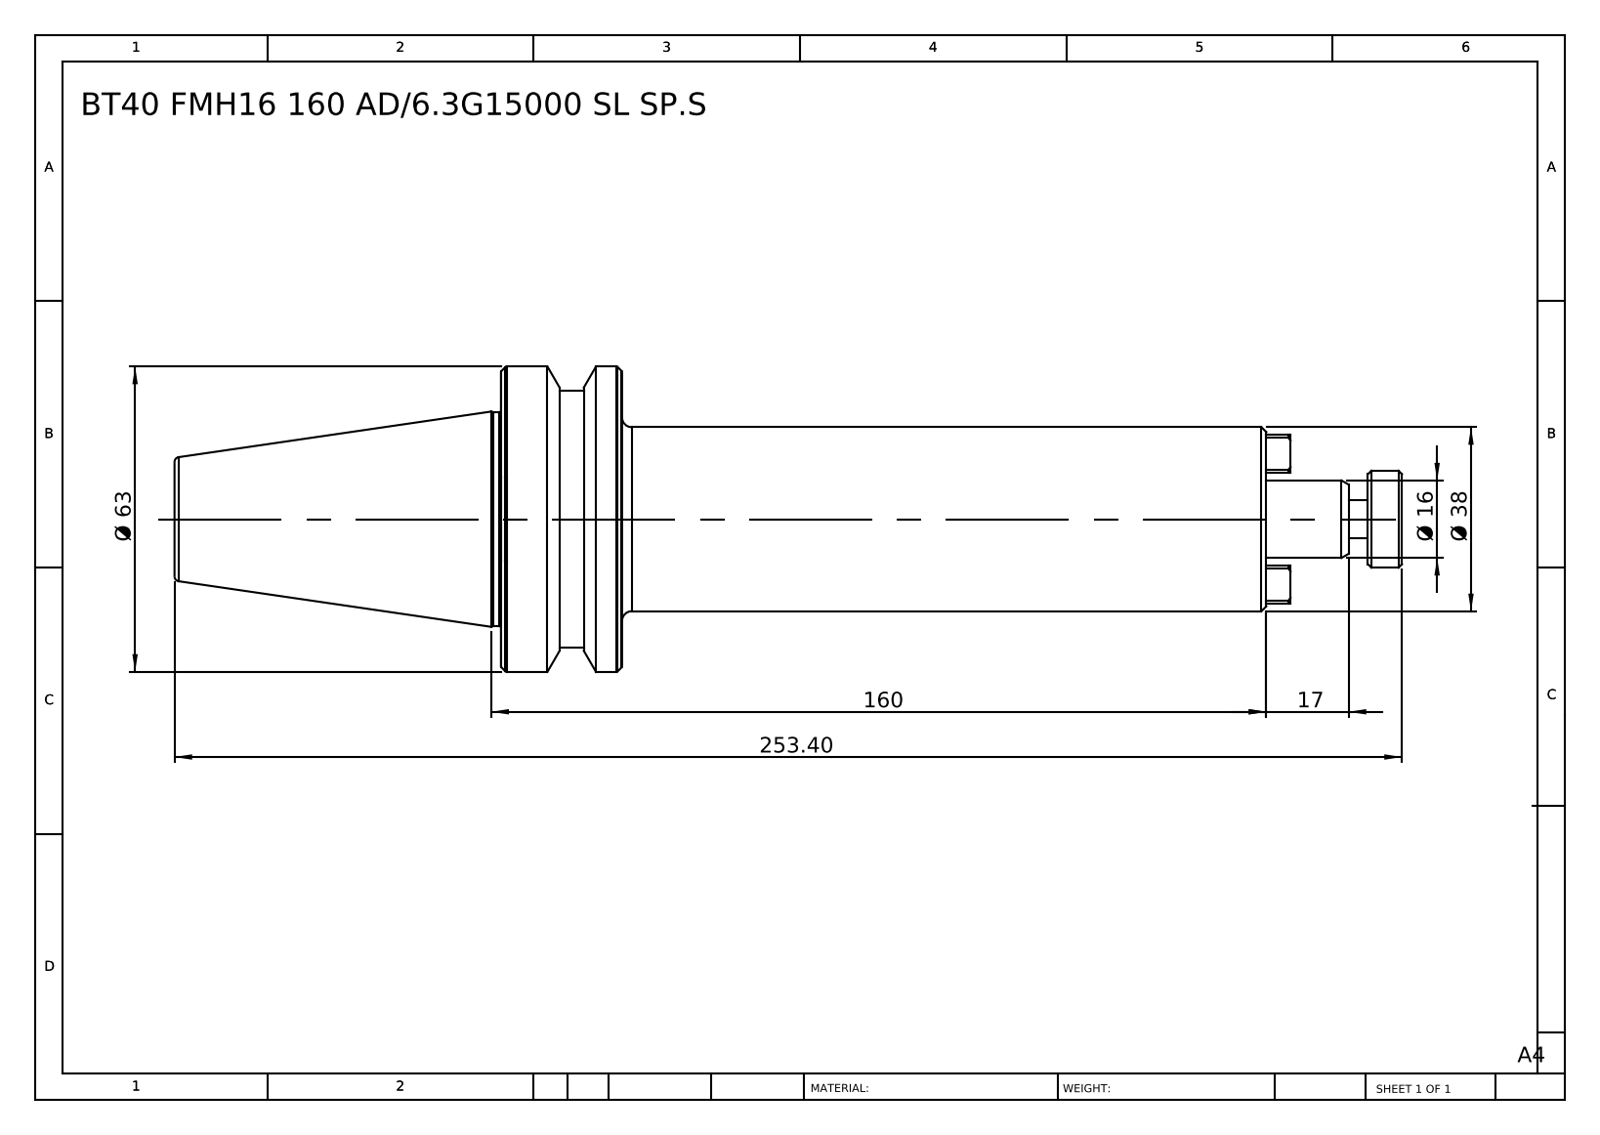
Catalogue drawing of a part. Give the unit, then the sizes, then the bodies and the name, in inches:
Units: inches
Overall size (bounding box): 9.976 × 2.48 × 2.48
Round bosses / shafts (diameter × count): ⌀2.48 ×1, ⌀2.087 ×1, ⌀1.732 ×1, ⌀1.496 ×1, ⌀0.787 ×1, ⌀0.63 ×1, ⌀0.315 ×1
Main face-to-face distances: 0.984, 5.236, 6.22, 8.874, 3.638, 2.654, 1.102, 6.339, 7.323, 9.976
Volume: 18.04 in³ · Surface area: 56.06 in²
Bodies: 1 solid, 91 faces (35 planar, 16 cylindrical, 40 other)
Part name (STEP PRODUCT): BT40 FMH16 160 AD-6.3G 15000 SL SP.S
STEP written by: SolidWorks 2014 (CONFIG_CONTROL_DESIGN)
